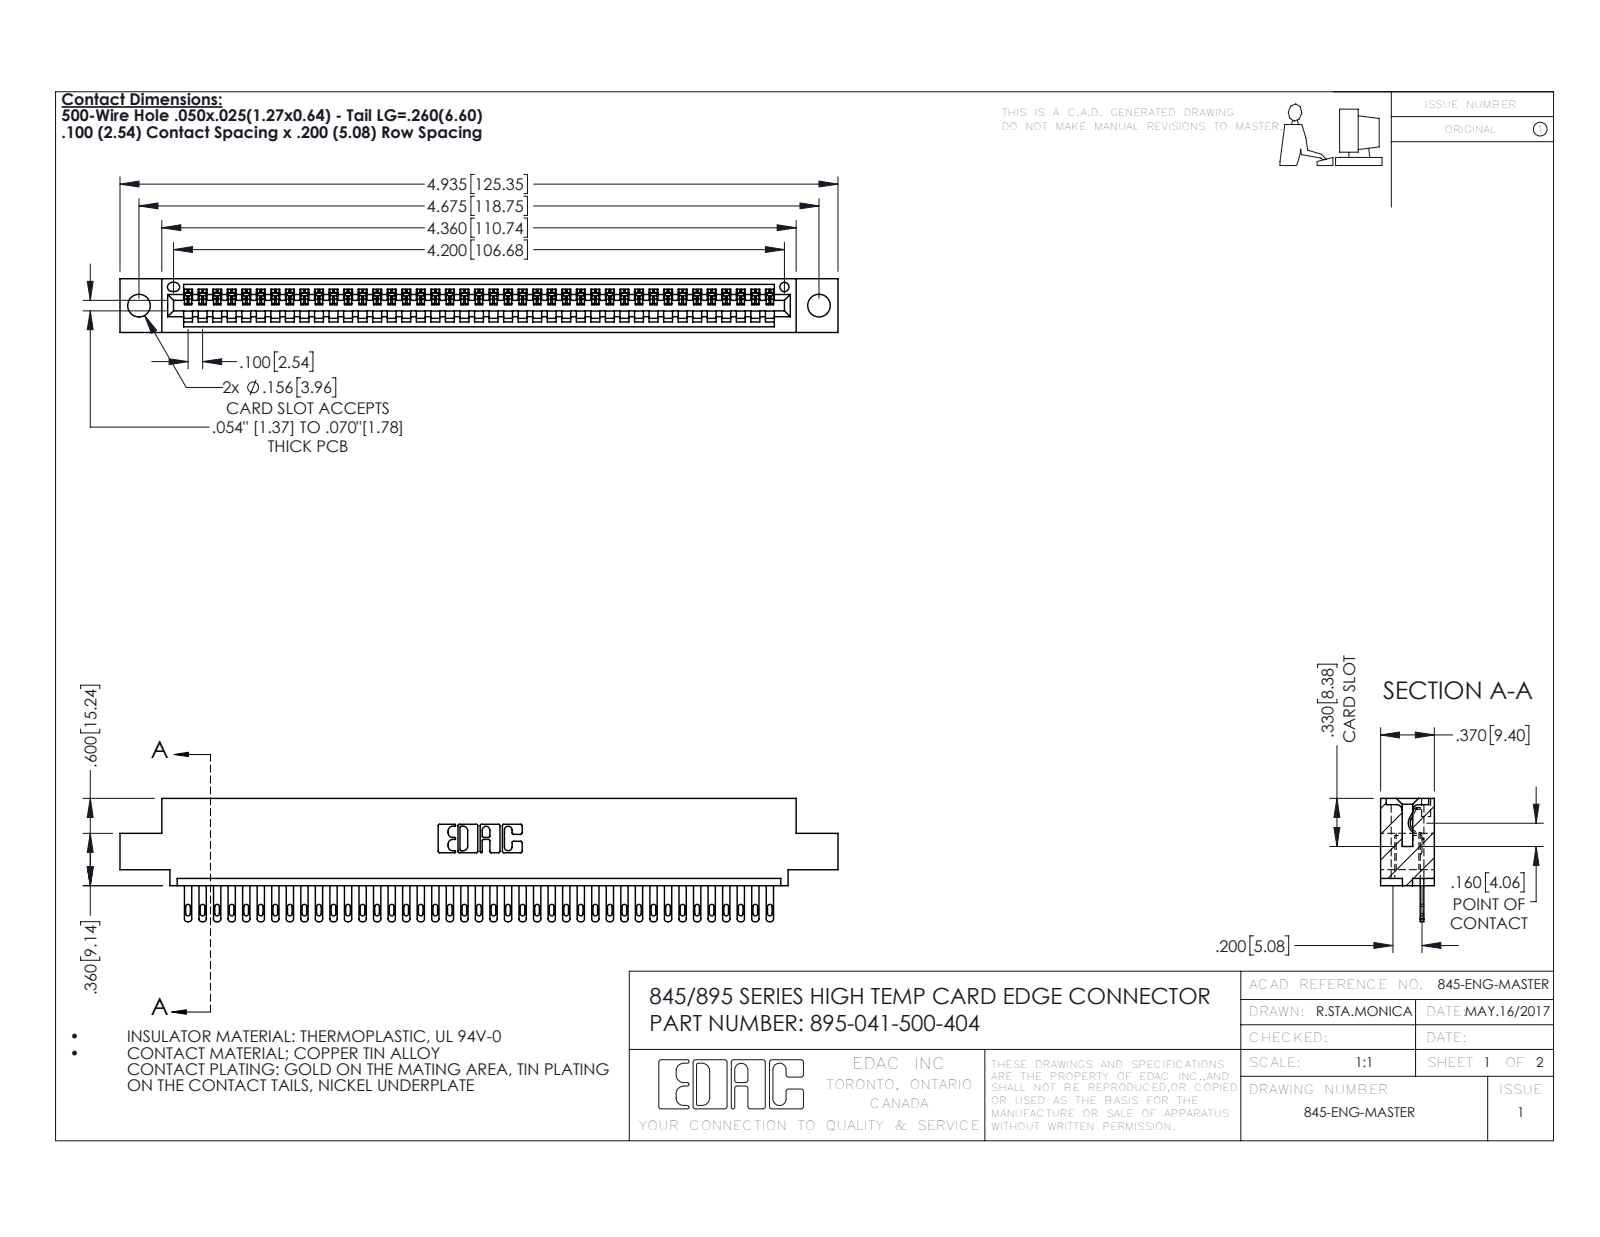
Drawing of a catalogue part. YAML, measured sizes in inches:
part_name: "845 Part_0.110 Offset - 0.156 Dia-TH; 345-292-001_345-293-100; 895-041-500-404"
step_written_by: "SolidWorks 2020 (CONFIG_CONTROL_DESIGN)"
units: inches
bodies: {solids: 42, faces: 2344, planar: 1478, cylindrical: 866, other: 0}
overall_size: [4.935, 0.847, 0.37]
volume: 0.718
surface_area: 24.18
round_holes:
  - {diameter: 0.156, count: 2}
  - {diameter: 0.064, count: 1}
partial_cylinders:
  - {radius: 0.006, count: 82}
  - {radius: 0.016, count: 82}
  - {radius: 0.02, count: 82}
  - {radius: 0.01, count: 22}
  - {radius: 0.007, count: 6}
  - {radius: 0.031, count: 6}
  - {radius: 0.026, count: 3}
  - {radius: 0.031, count: 2}
face_to_face_distances: [0.298, 0.072, 0.37, 0.098, 0.272, 0.025, 0.2, 0.225, 0.149, 0.072]
hole_center_spacings: [0.27, 4.439, 4.675]
